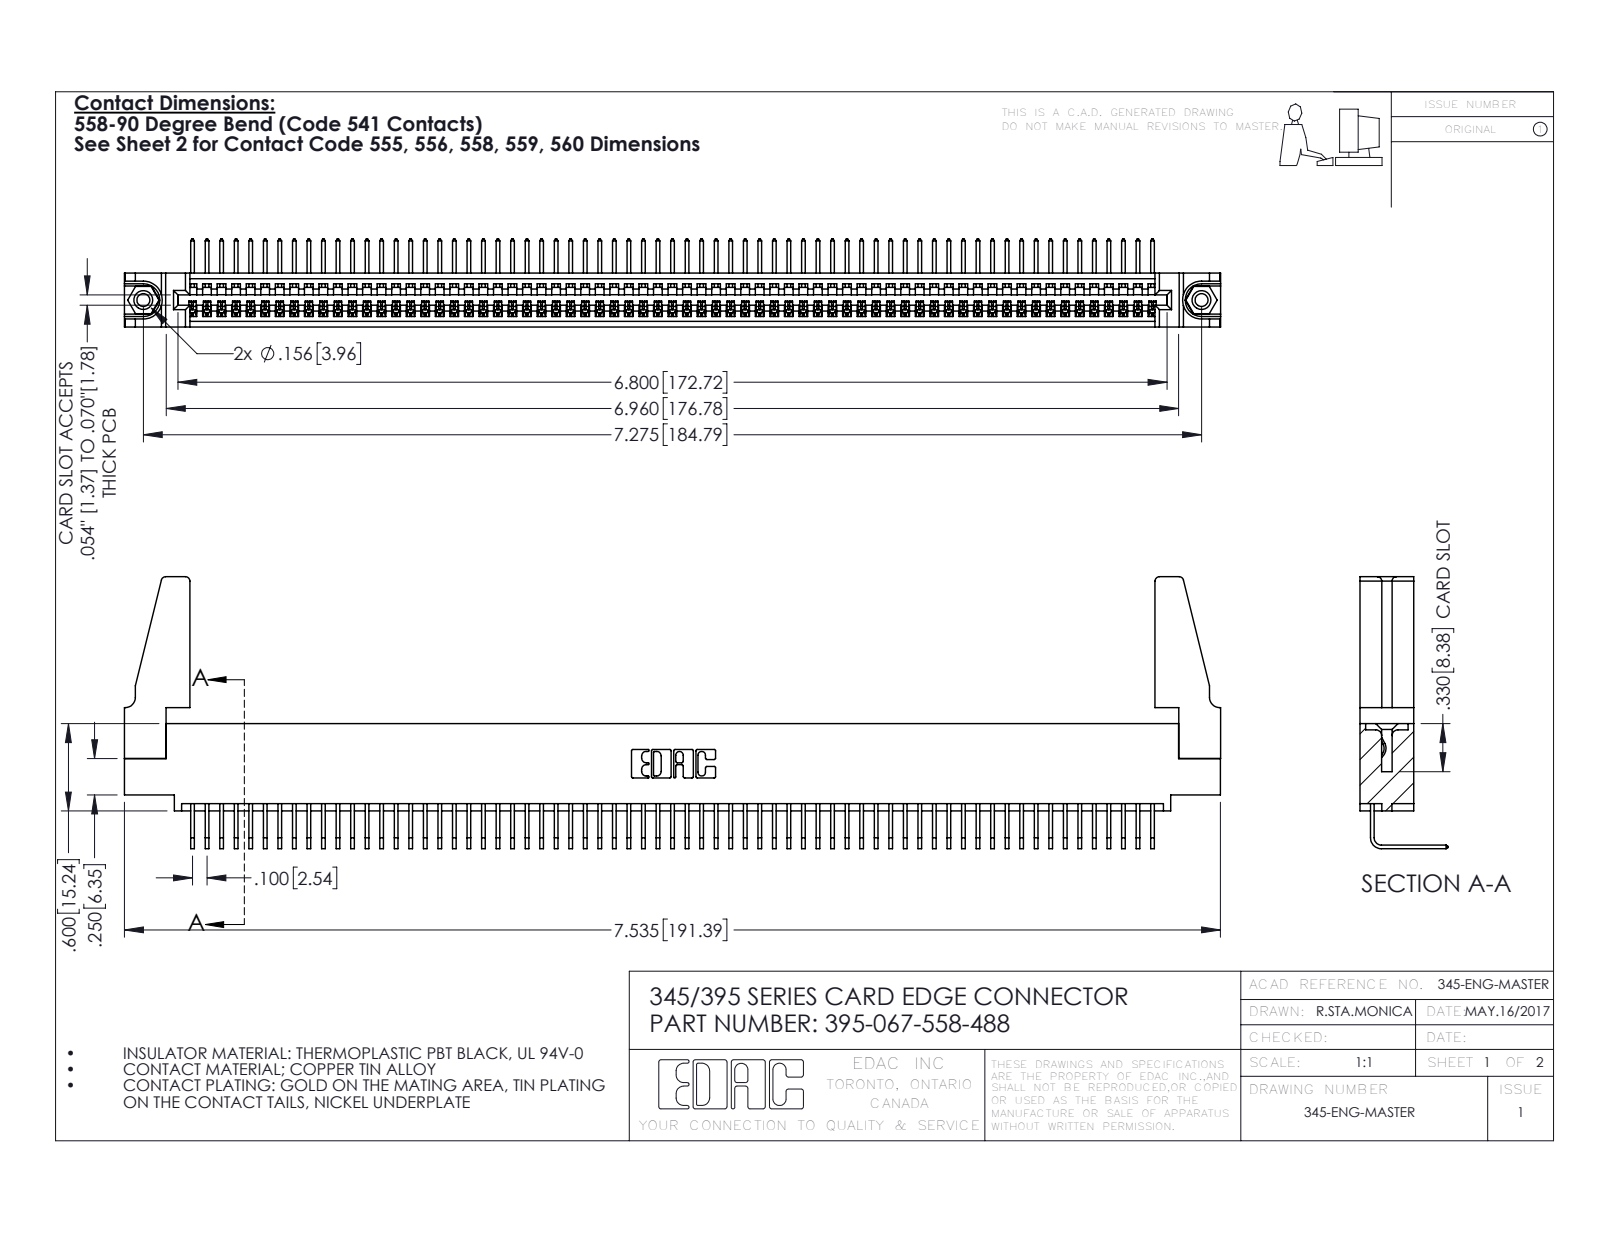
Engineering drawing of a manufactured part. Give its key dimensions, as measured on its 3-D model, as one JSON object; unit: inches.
{"part_name": "345-292-001_558 Tail - 2; 395-067-558-488; 345-220-078_345-220-088; 345-250-001_345-250-001-102 (+1 more)", "step_written_by": "SolidWorks 2016 (CONFIG_CONTROL_DESIGN)", "units": "inches", "bodies": {"solids": 72, "faces": 4274, "planar": 2970, "cylindrical": 1288, "other": 16}, "overall_size": [7.536, 1.869, 0.605], "volume_in3": 1.33, "surface_area_in2": 45.72, "round_holes": [[0.089, 2], [0.125, 2], [0.156, 2], [0.064, 1]], "round_bosses_or_shafts": [[0.155, 2]], "partial_cylinders_radius": [[0.006, 134], [0.01, 22], [0.03, 8], [0.007, 6], [0.031, 6], [0.026, 3], [0.031, 2], [0.04, 2]], "face_to_face_distances": [0.072, 0.298, 0.37, 0.098, 0.272, 0.025, 0.2, 0.225, 0.149, 0.072], "hole_center_spacings": [0.27, 7.039, 7.275]}
